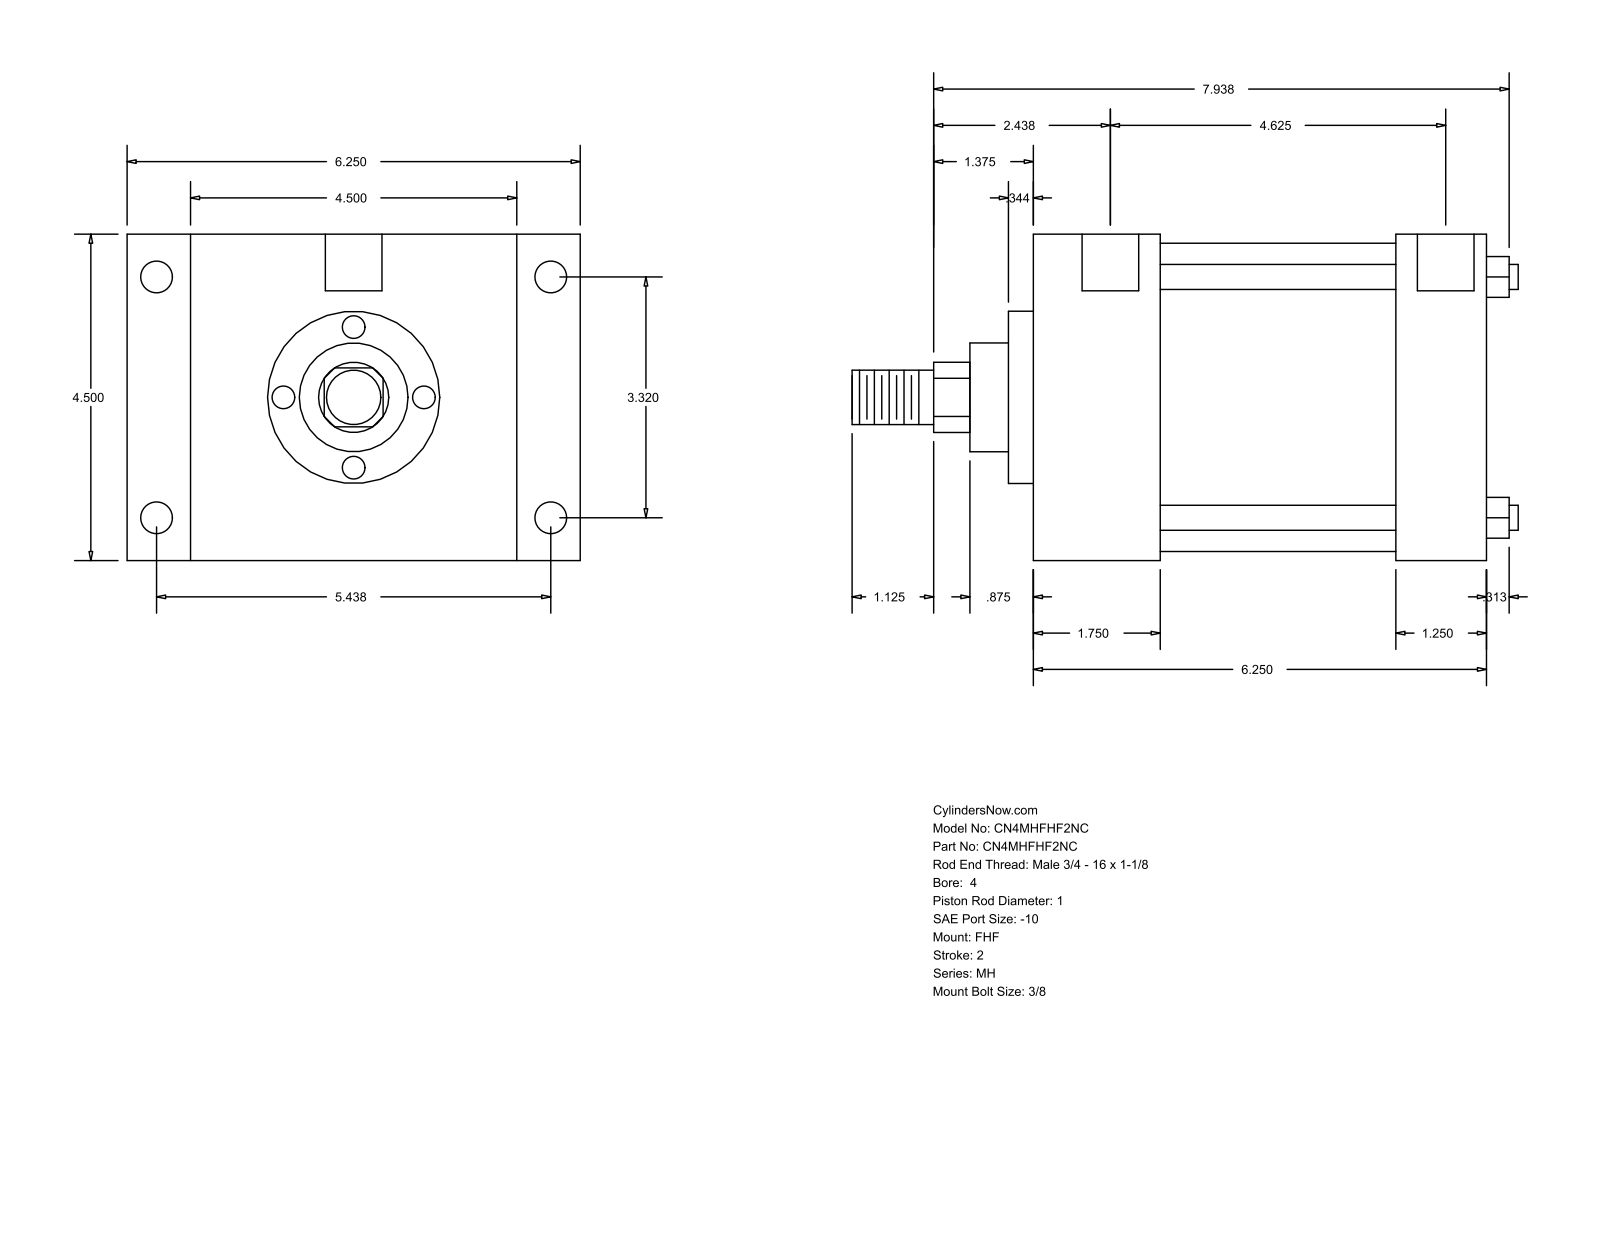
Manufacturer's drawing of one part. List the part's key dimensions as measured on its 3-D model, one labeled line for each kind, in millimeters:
Part name (STEP PRODUCT): MH_FHF__0400_1
STEP written by: GSSL Pune (CONFIG_CONTROL_DESIGN)
Units: millimetres
Bodies: 0 solids, 90 faces (61 planar, 29 cylindrical, 0 other)
Overall size (bounding box): 233.36 × 158.75 × 114.3
Round holes (diameter × count): ⌀8.73 ×4, ⌀11.13 ×4, ⌀19.84 ×2
Round bosses / shafts (diameter × count): ⌀8.76 ×4, ⌀107.95 ×1, ⌀60.33 ×1, ⌀38.1 ×1, ⌀25.4 ×1, ⌀19.05 ×1
Partial cylindrical surfaces — rounded edges, fillets, slot ends (radius × count): R12.29 ×1
Main face-to-face distances: 114.3, 158.76, 44.46, 22.23, 136.53, 127.01, 82.55, 31.75, 8.73, 53.19
Hole centre spacings: 1.58, 84.32, 119.06, 120.64, 138.12, 161.82, 117.48
